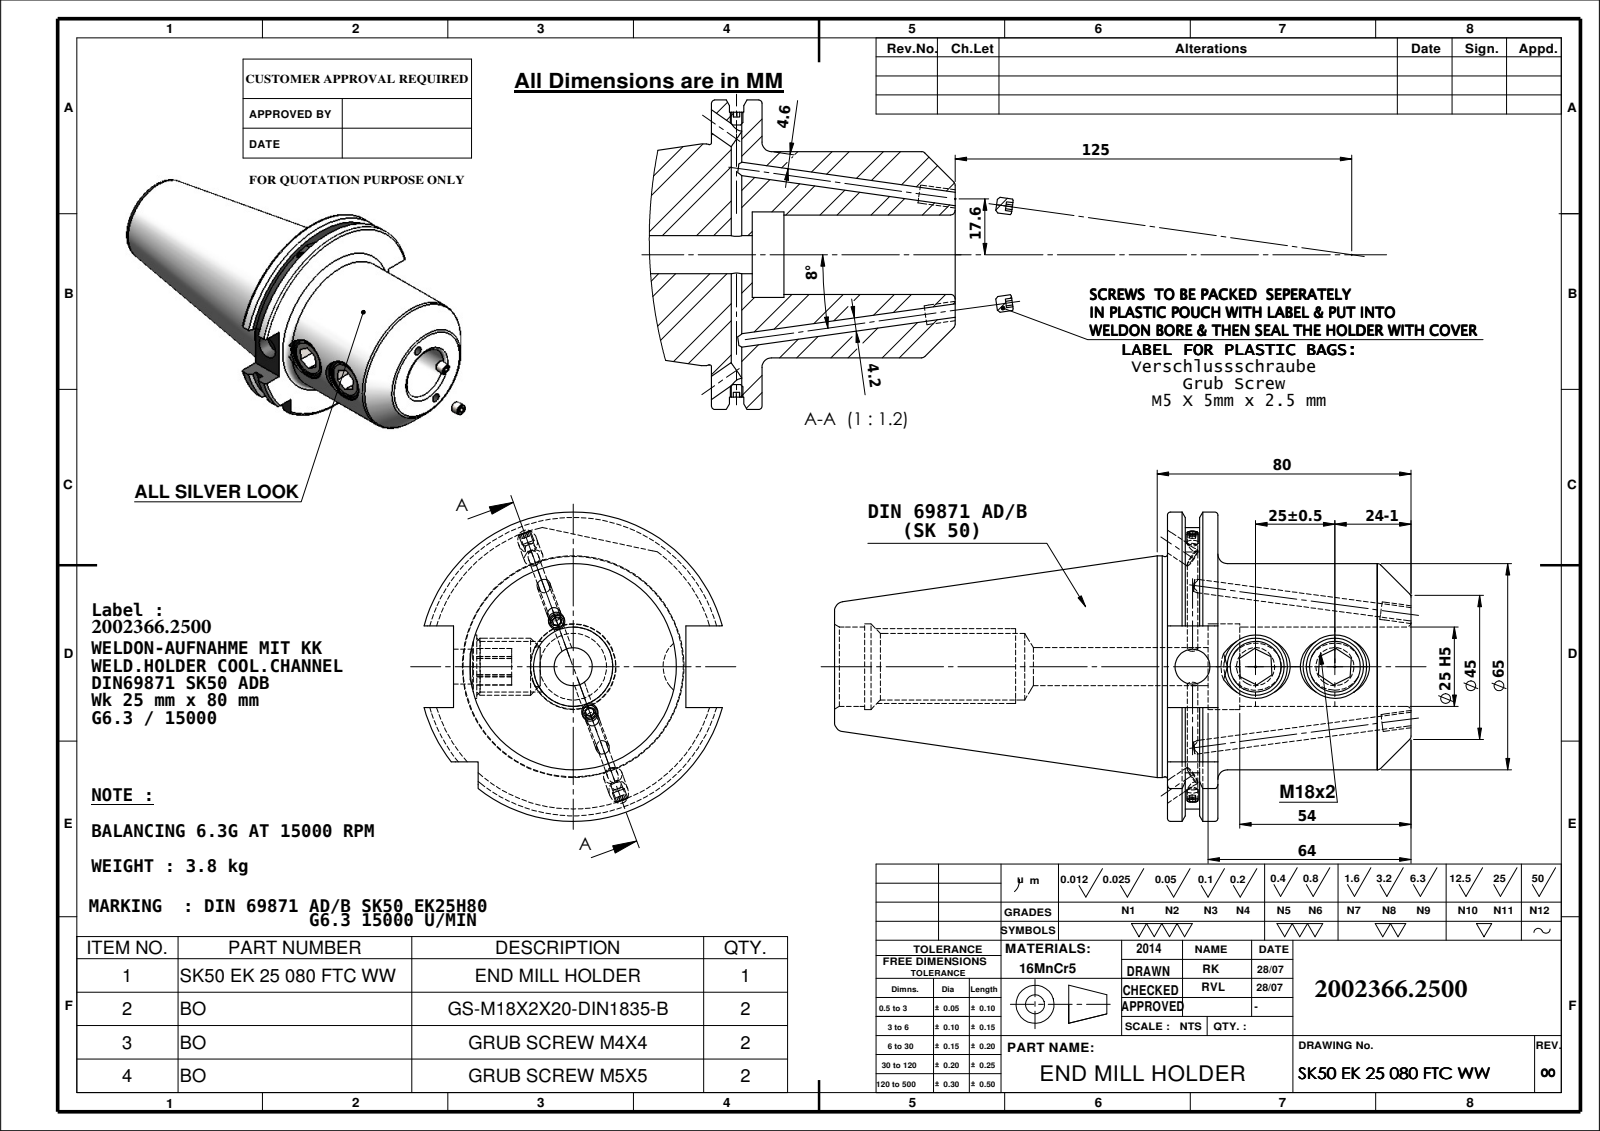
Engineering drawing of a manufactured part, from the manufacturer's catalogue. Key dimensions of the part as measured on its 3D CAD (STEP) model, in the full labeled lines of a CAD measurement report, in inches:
Part name (STEP PRODUCT): SK50 EK 25 080 FTC WW; Copy of M4X4_DIN 913 - M4 x 4-N; GS-M18X2X20; M5X5_DIN 913 - M5 x 5-N
STEP written by: SolidWorks 2009 (CONFIG_CONTROL_DESIGN)
Units: inches
Bodies: 7 solids, 233 faces (86 planar, 69 cylindrical, 78 other)
Overall size (bounding box): 7.876 × 3.839 × 3.703
Volume: 29.88 in³ · Surface area: 103.4 in²
Round holes (diameter × count): ⌀0.165 ×2, ⌀0.236 ×2, ⌀0.63 ×2, ⌀0.787 ×2, ⌀0.13 ×1, ⌀0.433 ×1, ⌀0.472 ×1, ⌀0.827 ×1, ⌀0.984 ×1, ⌀1.063 ×1
Round bosses / shafts (diameter × count): ⌀0.709 ×2, ⌀0.197 ×2, ⌀0.157 ×2, ⌀2.75 ×1, ⌀2.734 ×1, ⌀2.559 ×1
Partial cylindrical surfaces — rounded edges, fillets, slot ends (radius × count): R1.768 ×1, R1.919 ×1
Main face-to-face distances: 0.626, 3.024, 2.398, 0.4, 0.226, 2.624, 0.223, 0.177, 0.403, 2.801
Hole centre spacings: 0.783, 0.984, 1.768
